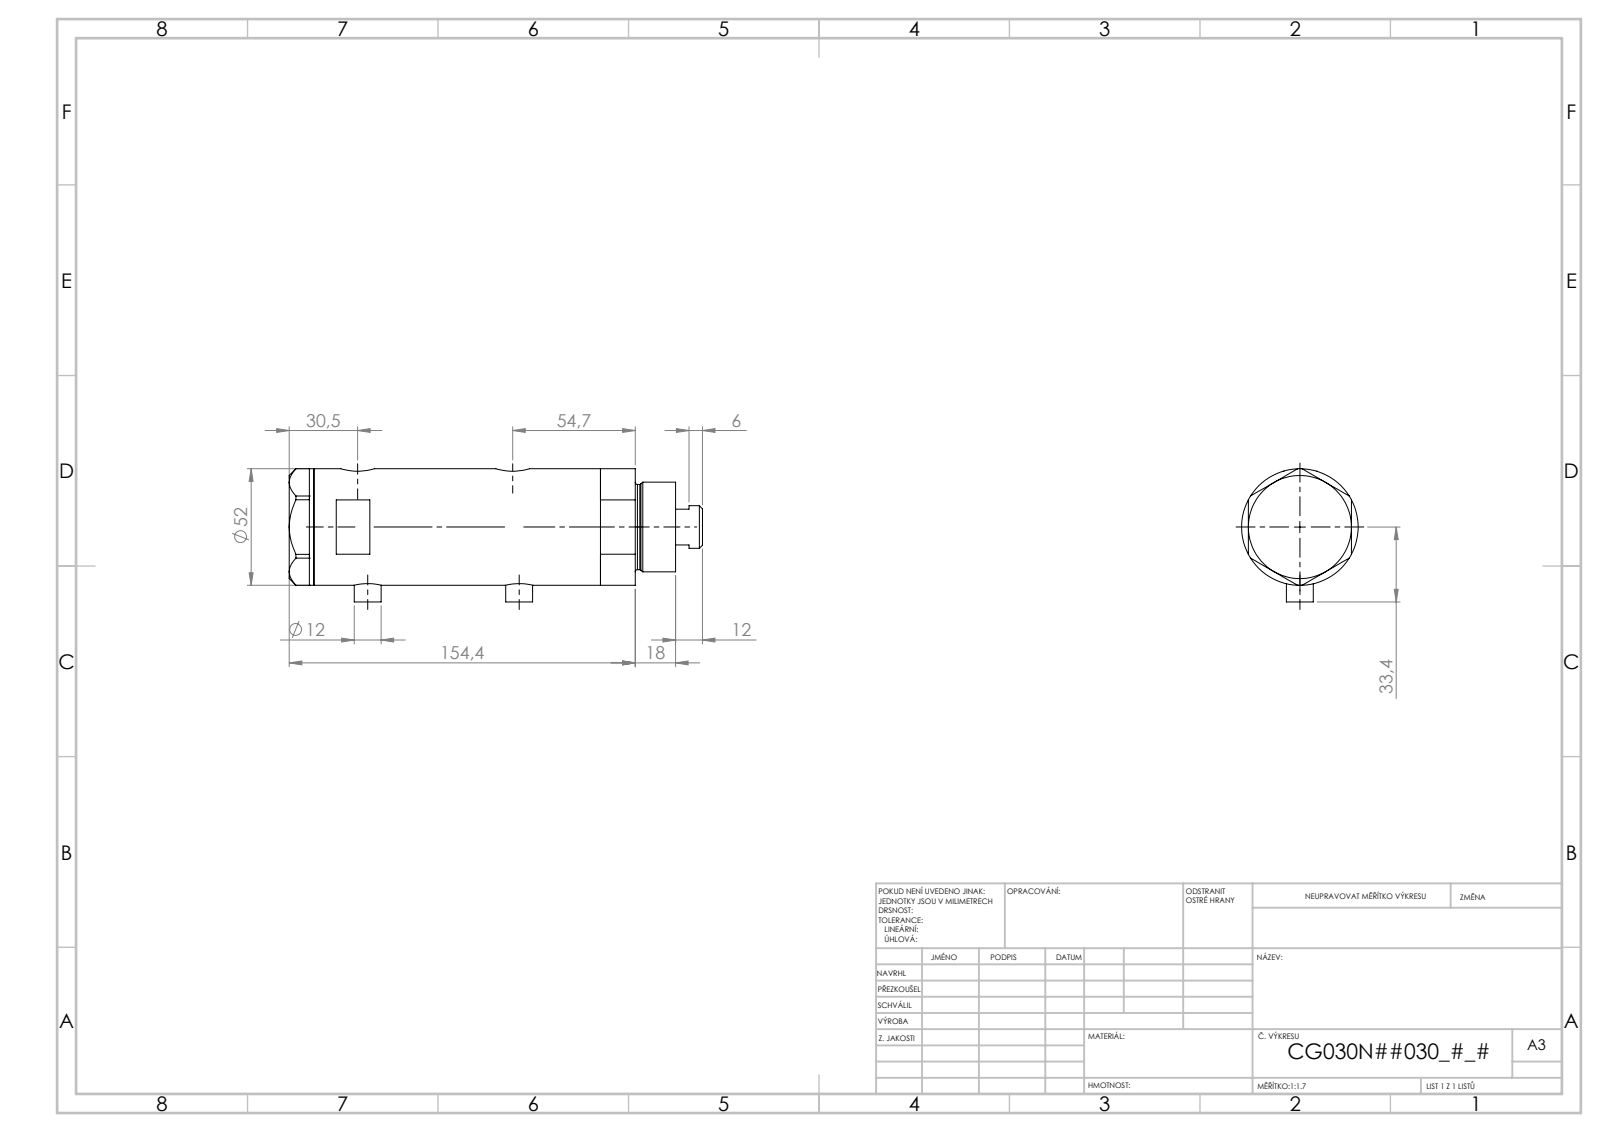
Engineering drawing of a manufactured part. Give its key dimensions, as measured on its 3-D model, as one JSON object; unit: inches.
{"part_name": "V270CG_FRONT; V270CG_VC; V270CG_MIDDLE; V270CG_BACK", "step_written_by": "SolidWorks 2019 (CONFIG_CONTROL_DESIGN)", "units": "inches", "bodies": {"solids": 4, "faces": 140, "planar": 67, "cylindrical": 53, "other": 20}, "overall_size": [7.048, 2.091, 2.047], "volume_in3": 19.49, "surface_area_in2": 115.8, "round_holes": [[0.197, 2], [0.383, 2], [0.492, 2], [0.591, 2], [0.256, 1], [0.787, 1], [0.846, 1], [1.181, 1], [1.299, 1], [1.732, 1]], "round_bosses_or_shafts": [[0.472, 2], [2.047, 1], [1.575, 1], [1.496, 1], [0.748, 1]], "face_to_face_distances": [0.937, 0.433, 1.37, 1.811, 3.722, 3.29, 2.352, 5.156, 4.723, 3.785], "hole_center_spacings": [0.114, 0.177, 2.234, 2.348, 2.411, 2.526, 0.114, 0.115]}
